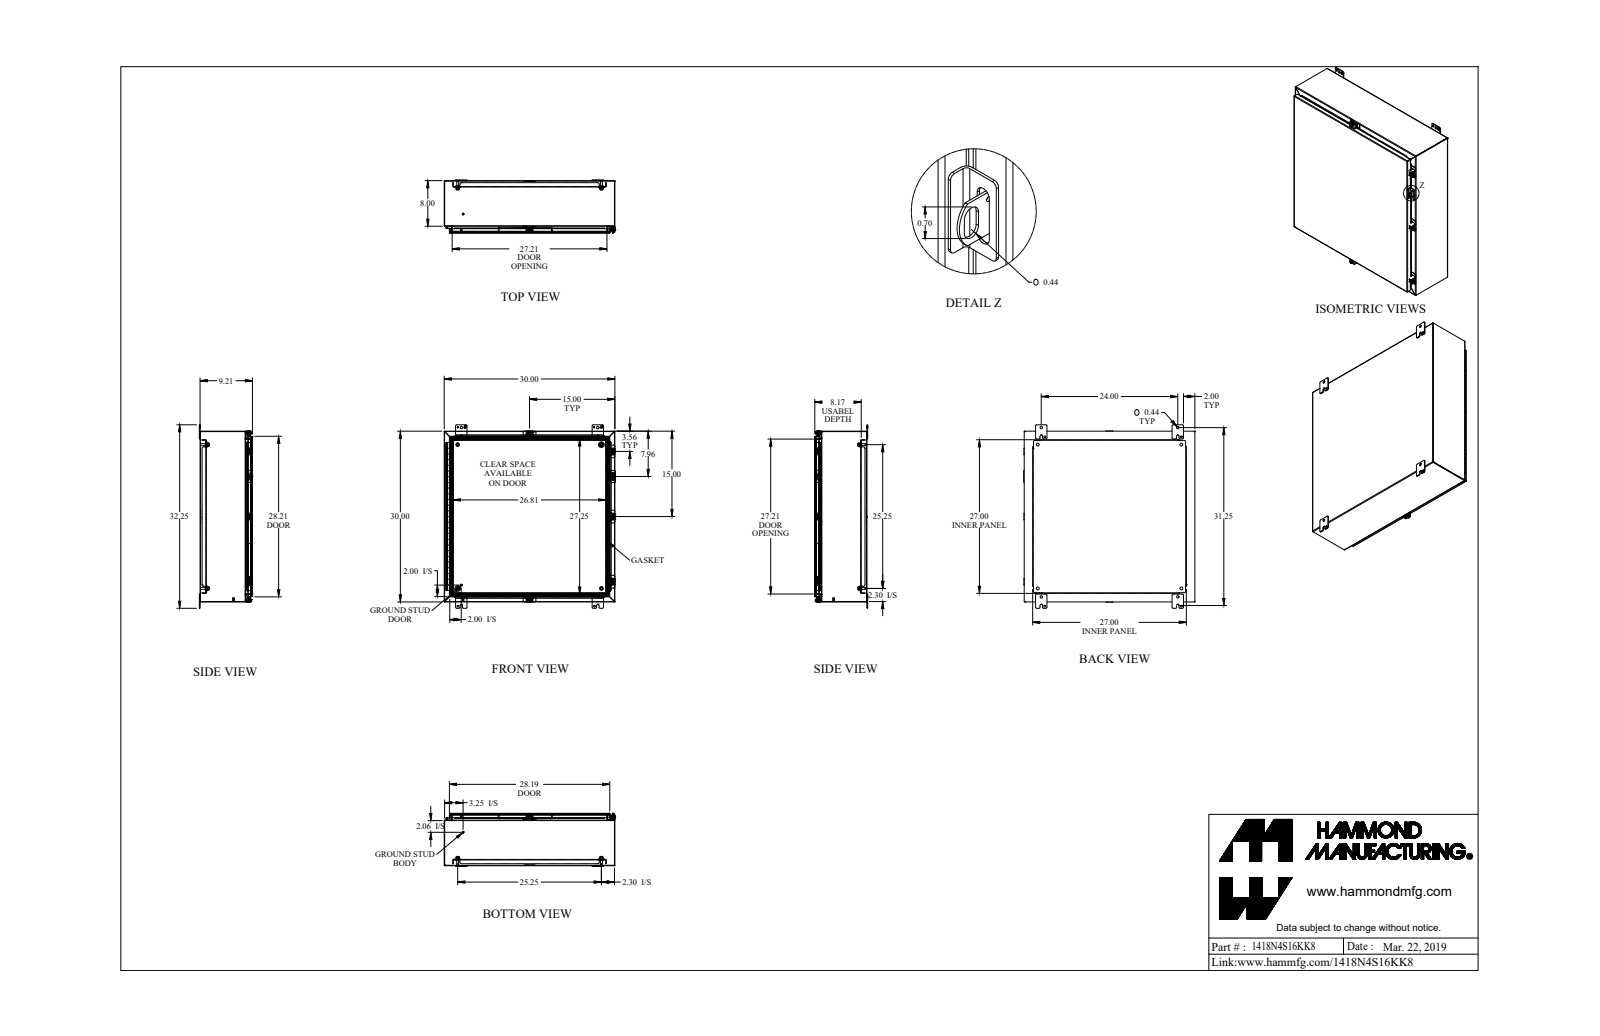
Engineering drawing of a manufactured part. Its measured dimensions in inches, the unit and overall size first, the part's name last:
Units: inches
Overall size (bounding box): 32.25 × 30.099 × 9.375
Round holes (diameter × count): ⌀0.213 ×5, ⌀0.265 ×5, ⌀0.375 ×5, ⌀0.313 ×4, ⌀0.437 ×4, ⌀0.5 ×4, ⌀0.307 ×2, ⌀0.445 ×2, ⌀0.11 ×1, ⌀0.125 ×1
Round bosses / shafts (diameter × count): ⌀0.5 ×5, ⌀0.39 ×5, ⌀0.244 ×5, ⌀0.65 ×4, ⌀0.375 ×4, ⌀0.332 ×4, ⌀1 ×2, ⌀0.313 ×2
Partial cylindrical surfaces — rounded edges, fillets, slot ends (radius × count): R0.25 ×32, R0.048 ×27, R0.143 ×27, R0.188 ×26, R0.036 ×24, R0.108 ×24, R0.125 ×14, R0.141 ×10
Main face-to-face distances: 0.072, 29.928, 0.072, 9.066, 9.138, 9.138, 0.095, 9.21, 8.106, 8.034
Hole centre spacings: 25.25, 30.146, 12.802, 1.736, 12.803, 24, 29.75, 35.709
Volume: 311.5 in³ · Surface area: 8 134 in²
Bodies: 43 solids, 1575 faces (847 planar, 588 cylindrical, 140 other)
Part name (STEP PRODUCT): 1418N4S16KK8_Default
STEP written by: SolidWorks 2019 (CONFIG_CONTROL_DESIGN)
